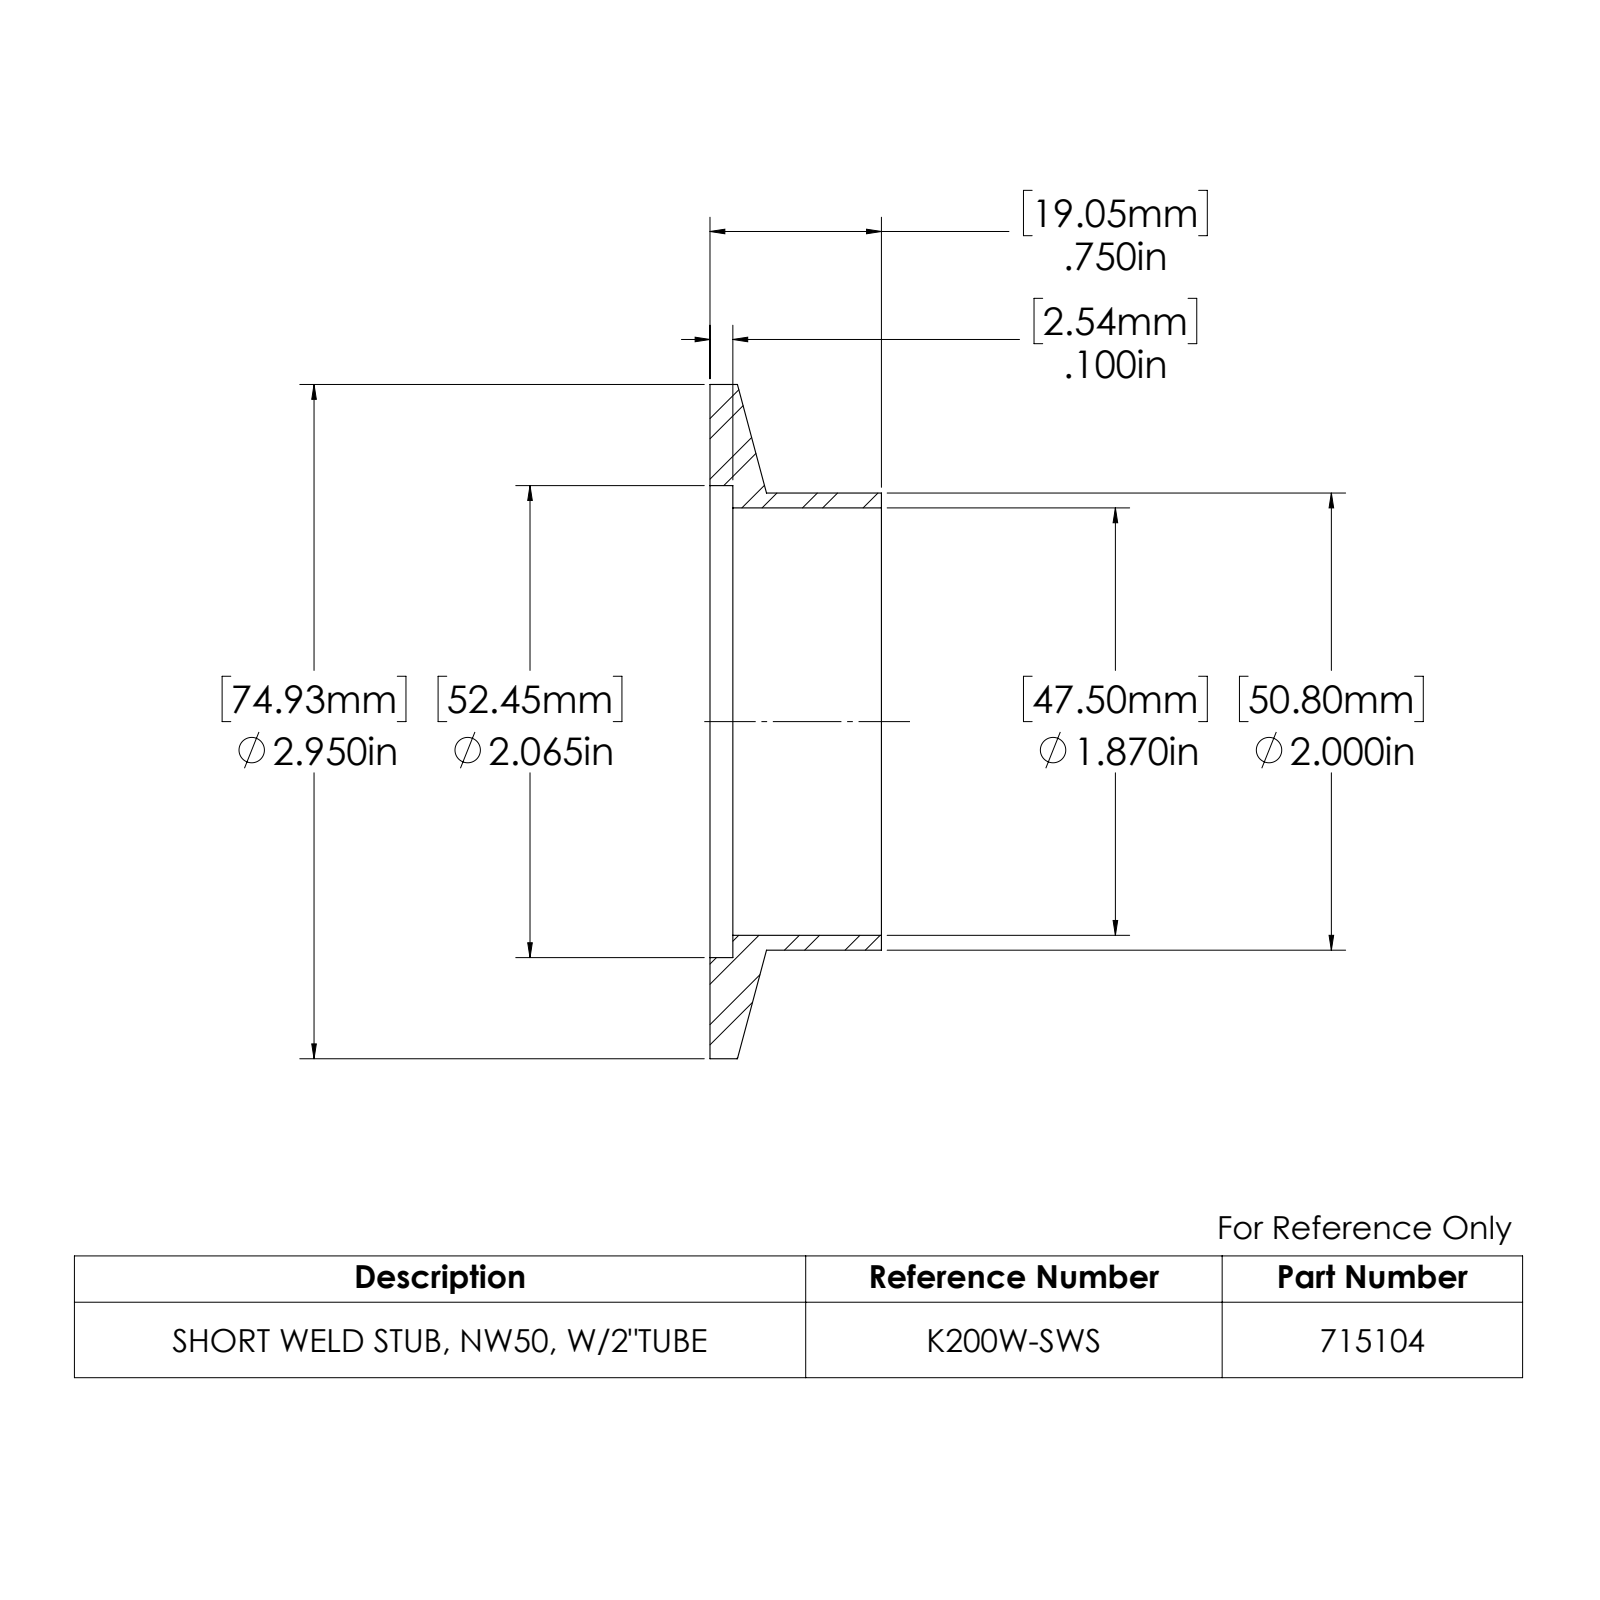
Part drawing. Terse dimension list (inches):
name: 715104
written by: SolidWorks 2022 (AUTOMOTIVE_DESIGN)
unit: in
bodies: 1 solid, 13 faces (3 planar, 8 cylindrical, 2 other)
size: 2.95 × 2.95 × 0.75
volume: 0.899 in³; area: 17.05 in²
holes: 1× ⌀1.87, 1× ⌀2.065
bosses: 1× ⌀2.95, 1× ⌀2
face distances: 0.1, 0.65, 0.75
